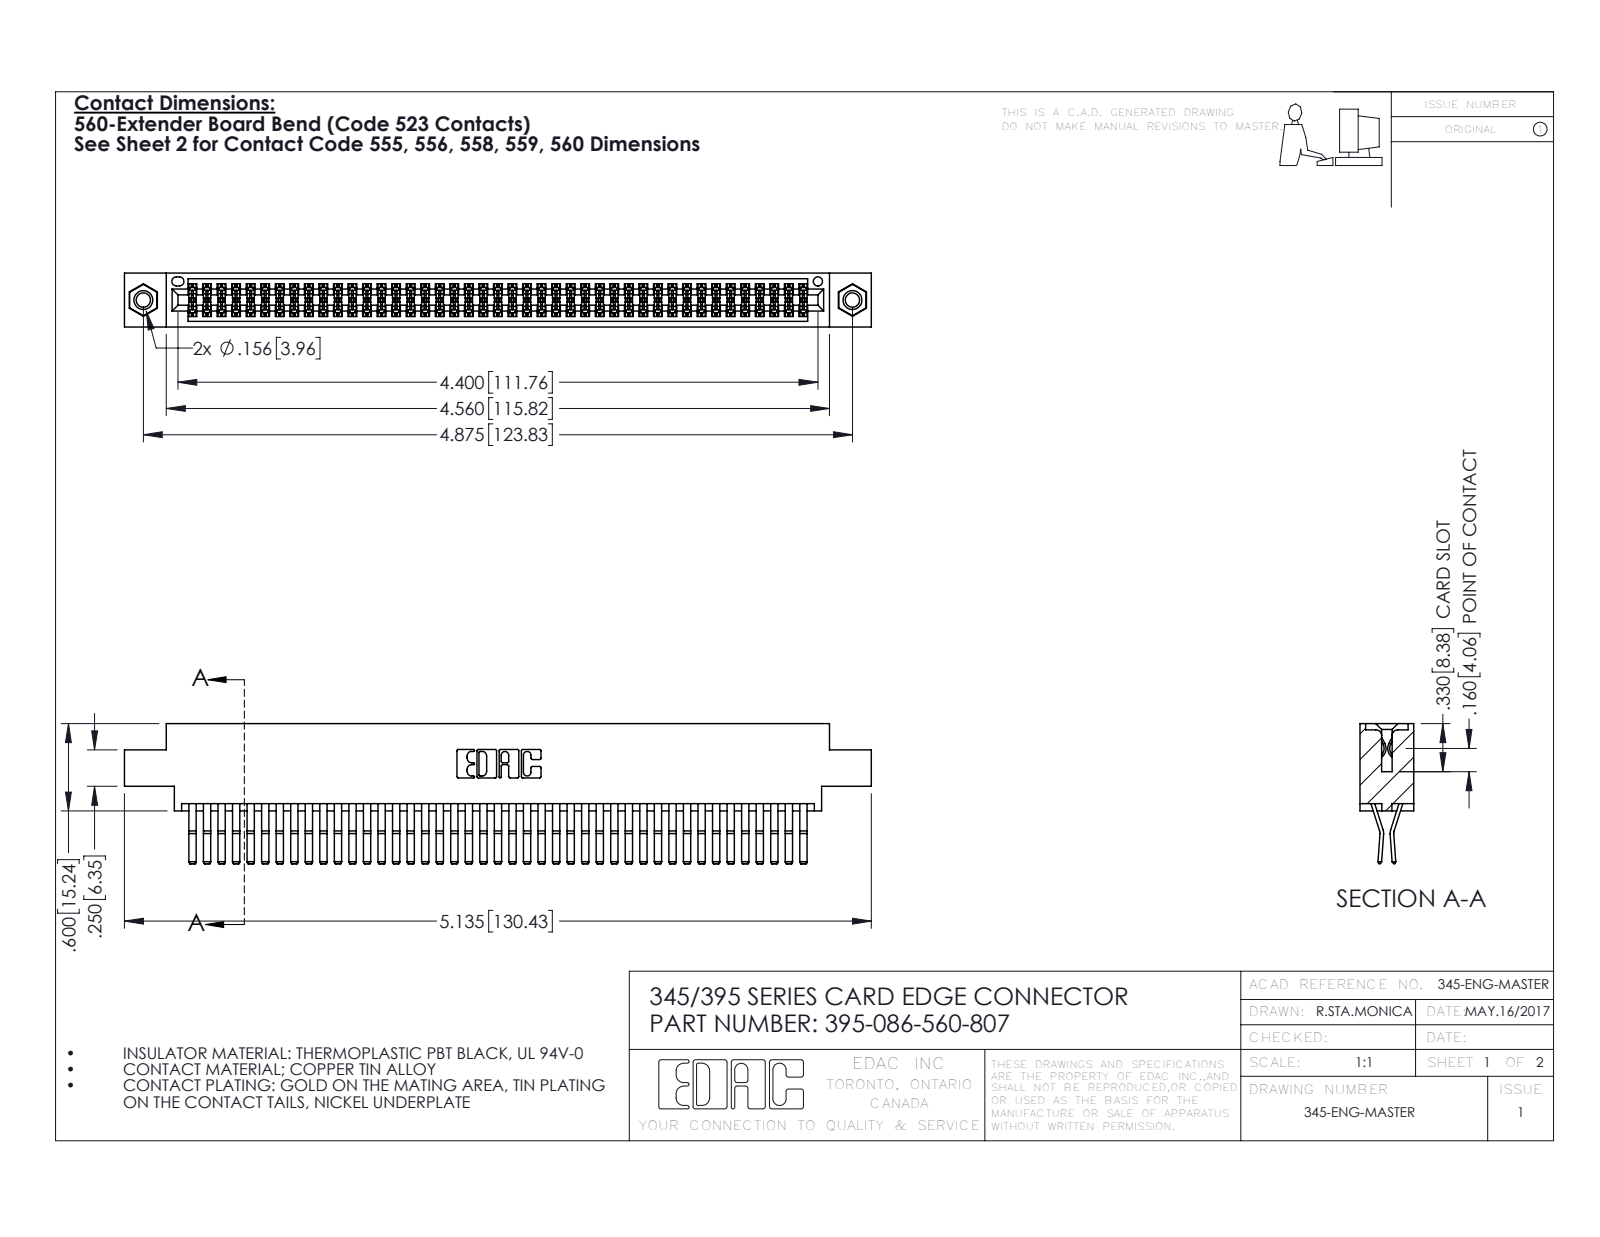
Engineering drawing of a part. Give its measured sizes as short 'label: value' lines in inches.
name: 345-250-001_345-250-005-103; 345-292-001_560 Tail; 345 Part_0.170 Offset - 0.156 Dia-TI; 395-086-560-807
written by: SolidWorks 2016 (CONFIG_CONTROL_DESIGN)
unit: in
bodies: 89 solids, 4662 faces (2954 planar, 1692 cylindrical, 16 other)
size: 5.135 × 0.962 × 0.37
volume: 0.8 in³; area: 32.59 in²
holes: 2× ⌀0.098, 2× ⌀0.125, 2× ⌀0.156, 1× ⌀0.064
bosses: 2× ⌀0.155
rounds: 130× R0.006, 22× R0.01, 6× R0.007, 6× R0.031, 3× R0.026, 2× R0.01, 2× R0.014, 2× R0.019
face distances: 0.025, 0.072, 0.298, 0.37, 0.2, 0.098, 0.272, 0.225, 0.175, 0.149
hole spacings: 0.27, 4.639, 4.875
